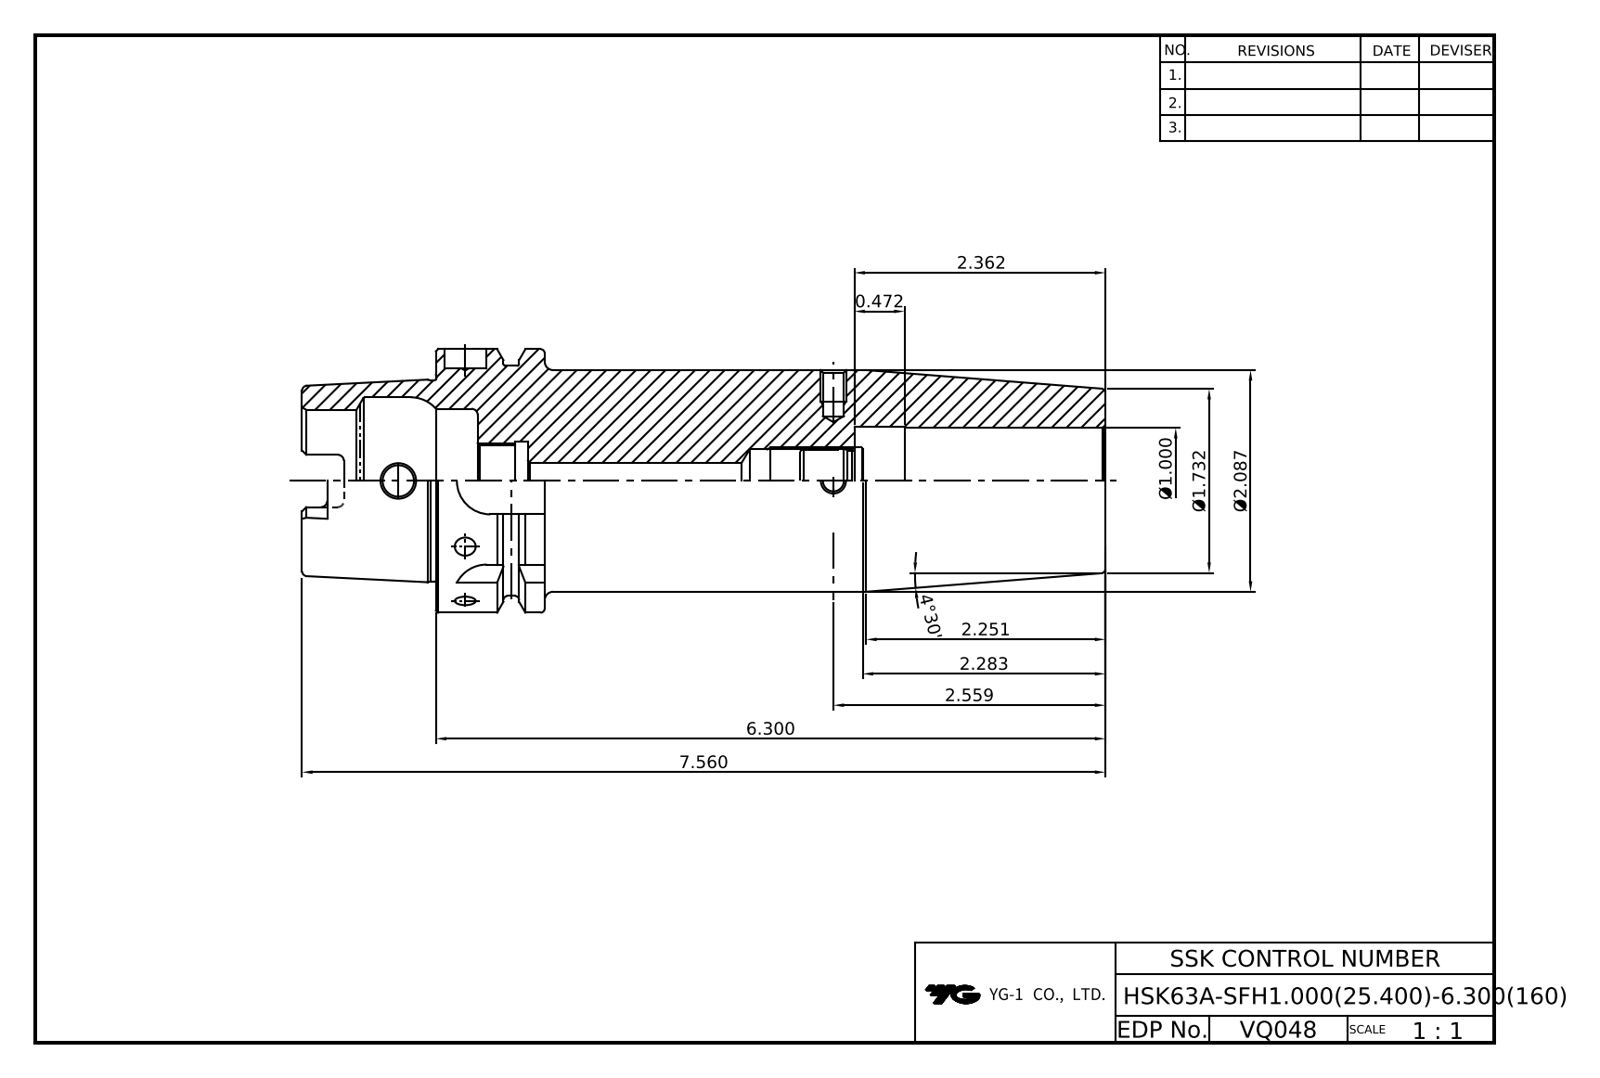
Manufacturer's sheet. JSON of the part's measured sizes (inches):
{"part_name": "LO-HSK63A-SFH25.4-160", "step_written_by": "Autodesk Inventor 2022 (AUTOMOTIVE_DESIGN)", "units": "inches", "bodies": {"solids": 1, "faces": 119, "planar": 44, "cylindrical": 34, "other": 41}, "overall_size": [7.559, 2.48, 2.48], "volume_in3": 19.47, "surface_area_in2": 77.9, "round_holes": [[0.295, 1], [0.315, 1], [0.394, 1], [0.587, 1], [0.666, 1], [0.748, 1], [1, 1], [1.047, 1], [1.339, 1], [1.575, 1]], "round_bosses_or_shafts": [[2.48, 1], [2.165, 1], [2.087, 1], [1.891, 1]], "partial_cylinders_radius": [[0.059, 6], [0.113, 4], [0.315, 4]], "face_to_face_distances": [6.299, 0.394, 5.906, 1.26, 1.024, 3.543, 5.276, 0.63, 3.937, 2.362]}
